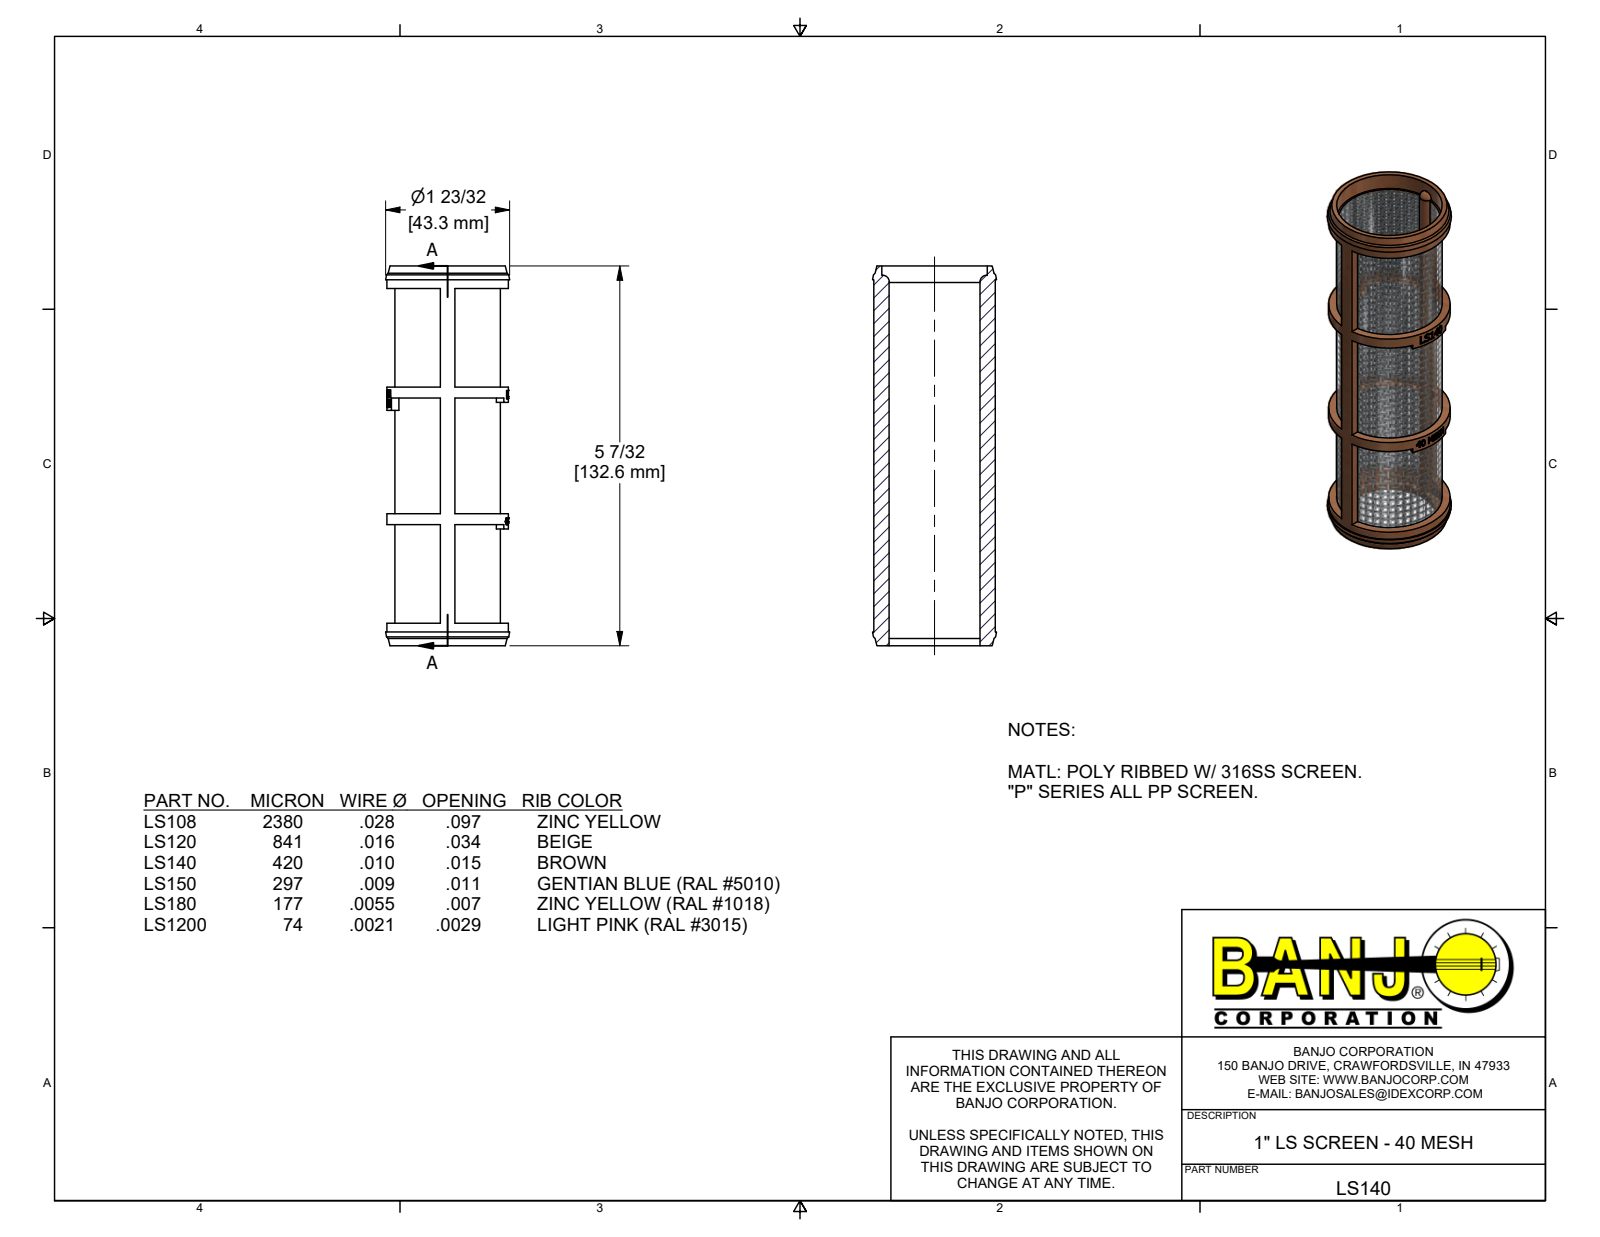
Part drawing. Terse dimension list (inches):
name: LS140
written by: Autodesk Inventor 2019 (AUTOMOTIVE_DESIGN)
unit: in
bodies: 1 solid, 381 faces (256 planar, 44 cylindrical, 81 other)
size: 5.22 × 1.705 × 1.705
volume: 1.373 in³; area: 54.95 in²
holes: 1× ⌀1.25, 1× ⌀1.4
bosses: 1× ⌀1.67, 1× ⌀1.45
rounds: 2× R0.1, 1× R0.815
face distances: 0.2, 1.74, 1.815, 3.555, 0.15, 1.665, 3.405, 0.31, 1.505, 3.245
